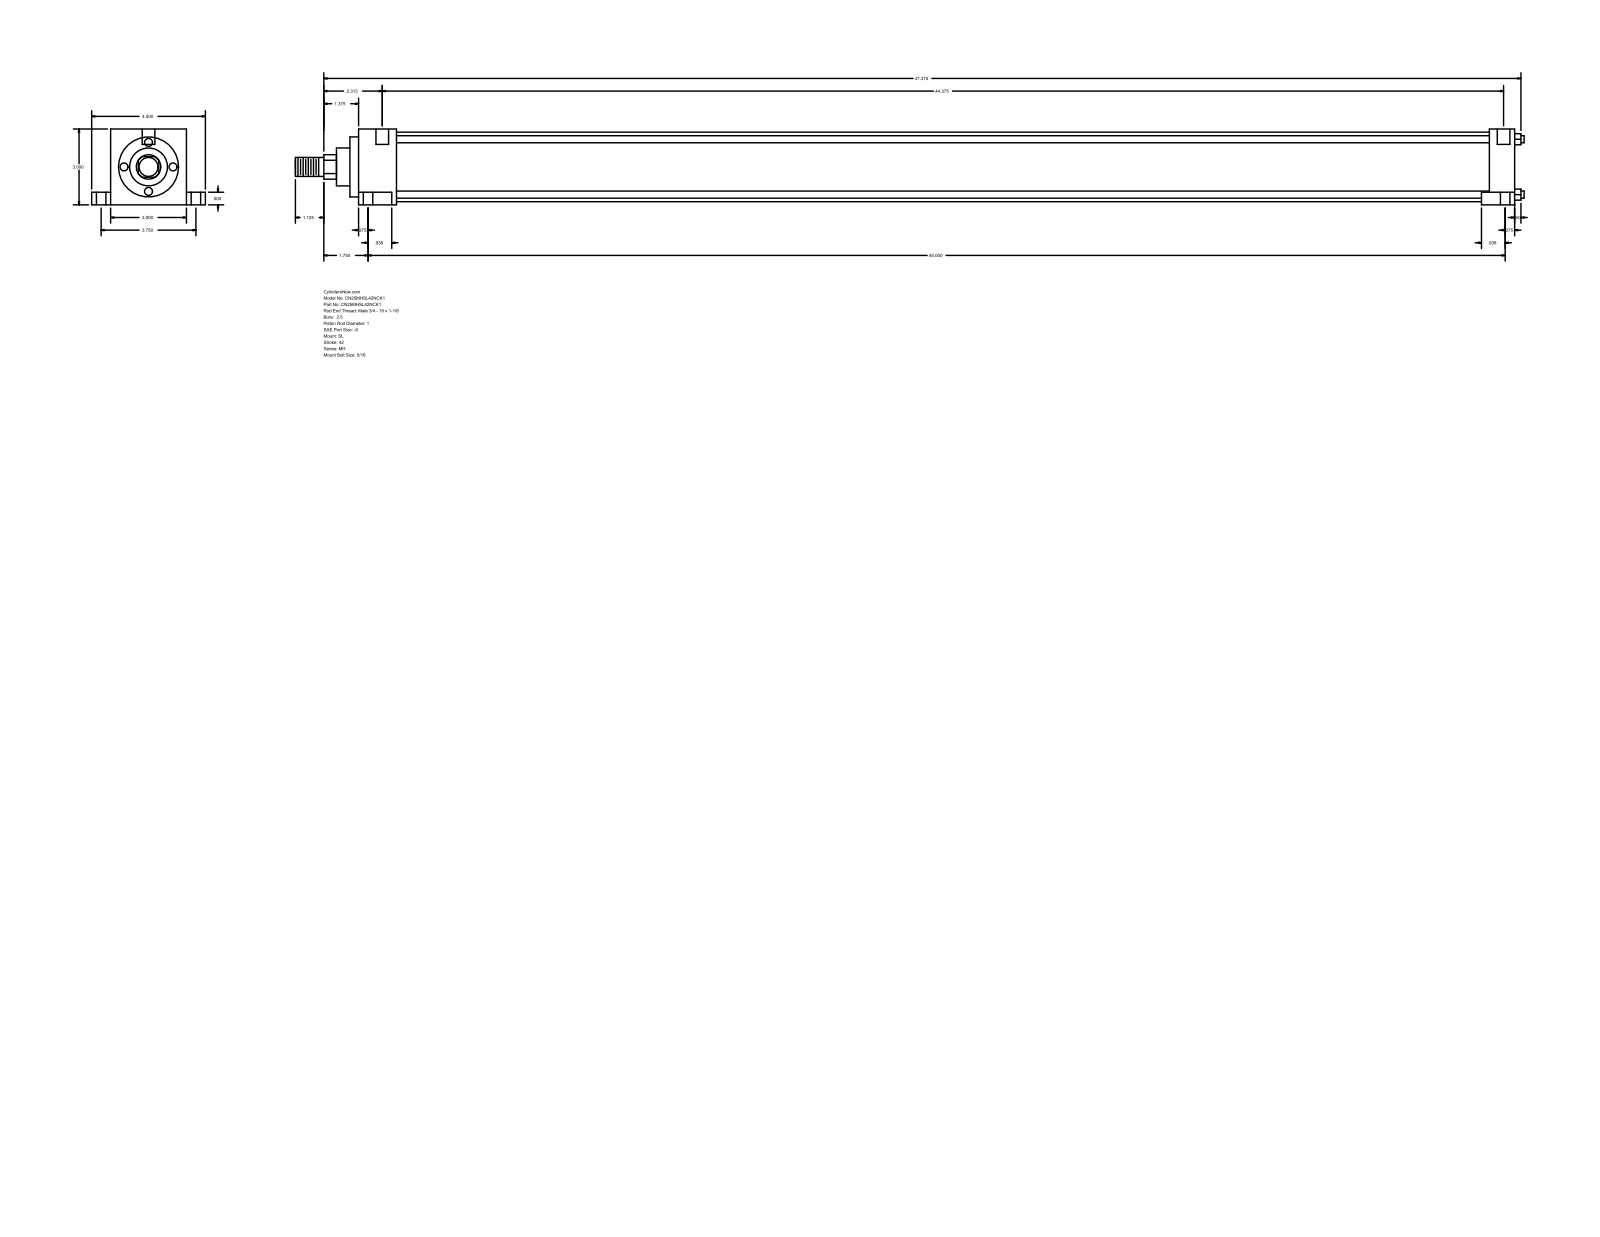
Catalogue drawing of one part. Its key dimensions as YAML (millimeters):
part_name: "MH_SL__0250_1"
step_written_by: "GSSL Pune (CONFIG_CONTROL_DESIGN)"
units: millimeters
bodies: {solids: 0, faces: 86, planar: 61, cylindrical: 25, other: 0}
overall_size: [1235.08, 114.3, 76.2]
round_holes:
  - {diameter: 5.56, count: 2}
  - {diameter: 9.53, count: 2}
  - {diameter: 15.88, count: 2}
  - {diameter: 12.7, count: 1}
round_bosses_or_shafts:
  - {diameter: 7.14, count: 4}
  - {diameter: 69.85, count: 1}
  - {diameter: 60.33, count: 1}
  - {diameter: 38.1, count: 1}
  - {diameter: 25.4, count: 1}
  - {diameter: 19.05, count: 1}
partial_cylinders:
  - {radius: 12.29, count: 1}
face_to_face_distances: [76.2, 25.39, 1145.39, 1170.78, 12.7, 63.5, 19.05, 95.25, 13.49, 1158.88]
hole_center_spacings: [47.65, 3.18, 95.24]
